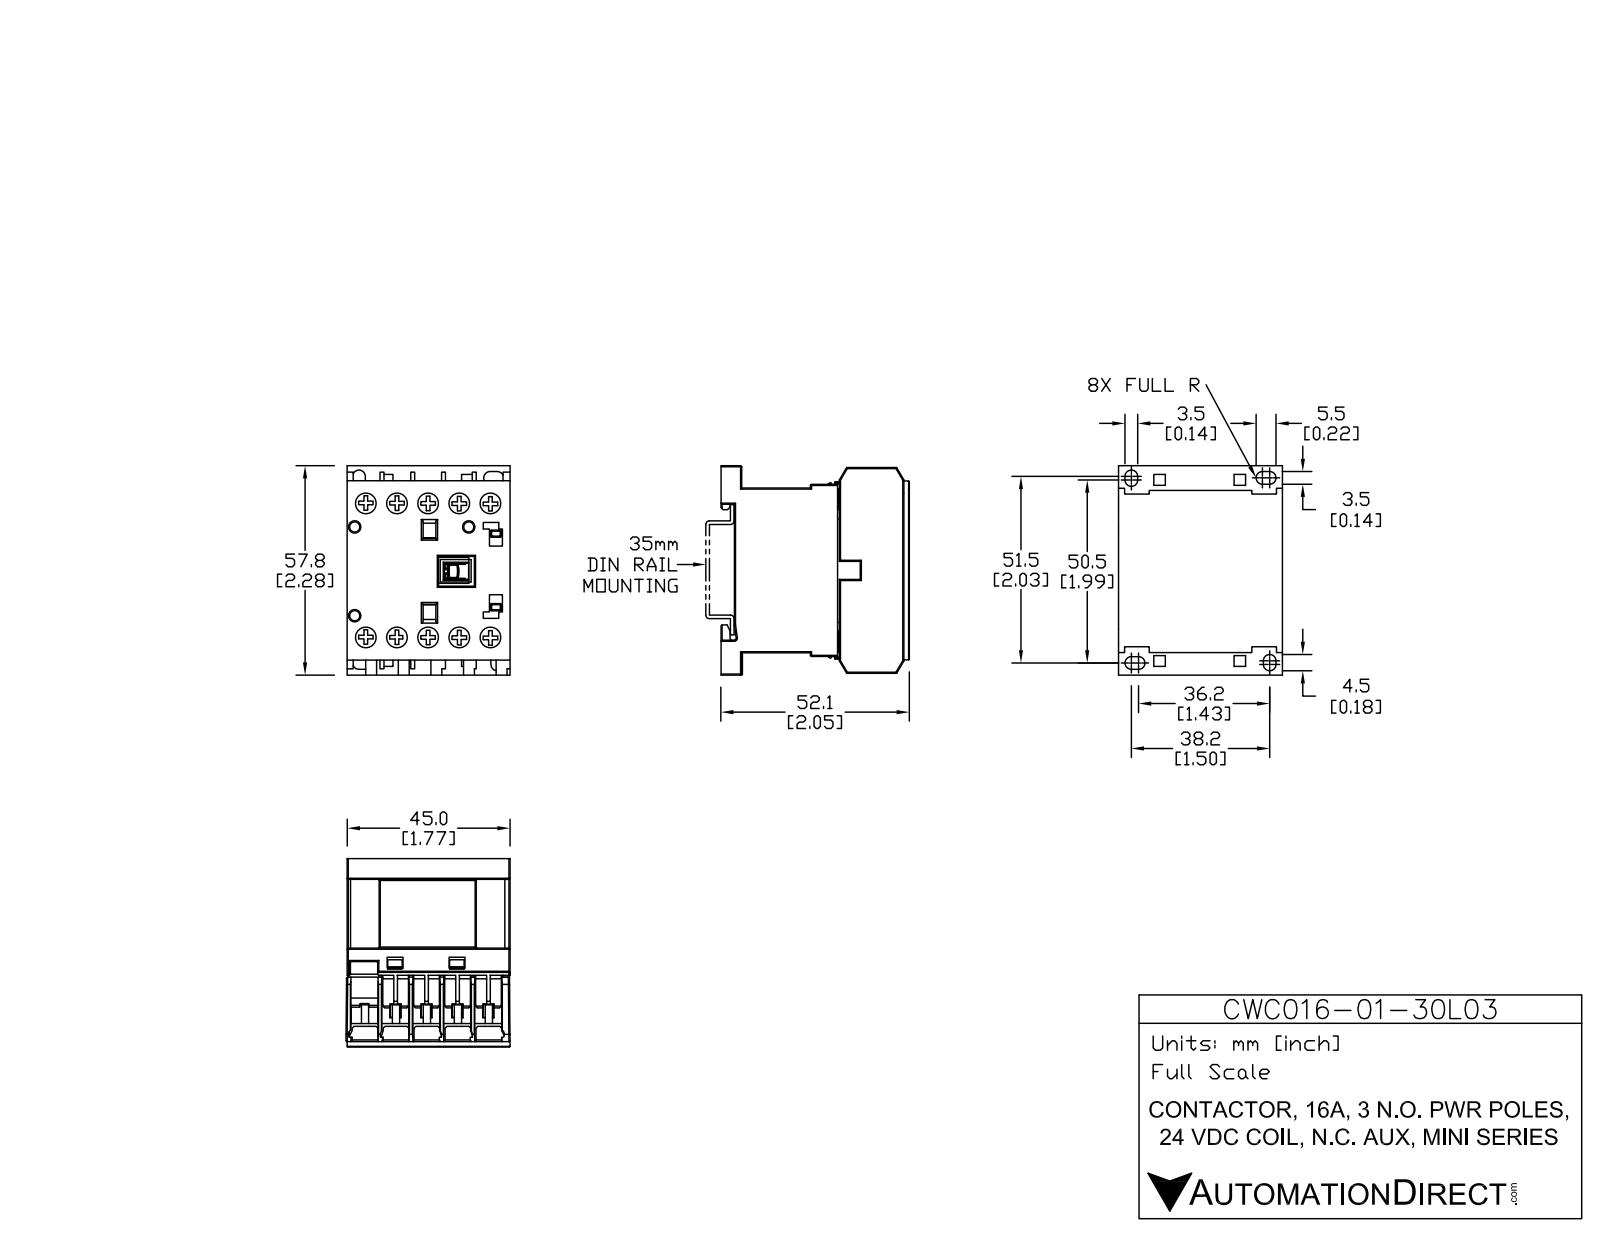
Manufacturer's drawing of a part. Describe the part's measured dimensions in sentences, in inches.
The part is named "CWC16-01-30L03". Its 3-D file was written by "SolidWorks 2013 (AUTOMOTIVE_DESIGN)". It is 15 solids with 535 faces: 445 planar, 90 cylindrical and 0 other. Overall it measures 2.285 by 2.052 by 1.801 inches. Its volume is 5.927 cubic inches and its surface area 47.18 square inches. Round holes: 10 of diameter 0.244, 3 of diameter 0.11. Round bosses or shafts: 10 of diameter 0.232. Partial cylindrical surfaces (rounded edges, fillets, slot ends): 20 of radius 0.012, 6 of radius 0.068, 2 of radius 0.068, 1 of radius 0.013, 1 of radius 0.017, 1 of radius 0.022. The main face-to-face distances are 0.325, 1.791, 0.049, 0.65, 0.374, 0.217, 0.699, 0.202, 0.419, 0.276. The hole center spacings are 0.337, 1.494, 0.673, 1.603, 1.455, 1.01, 1.771, 0.272.
